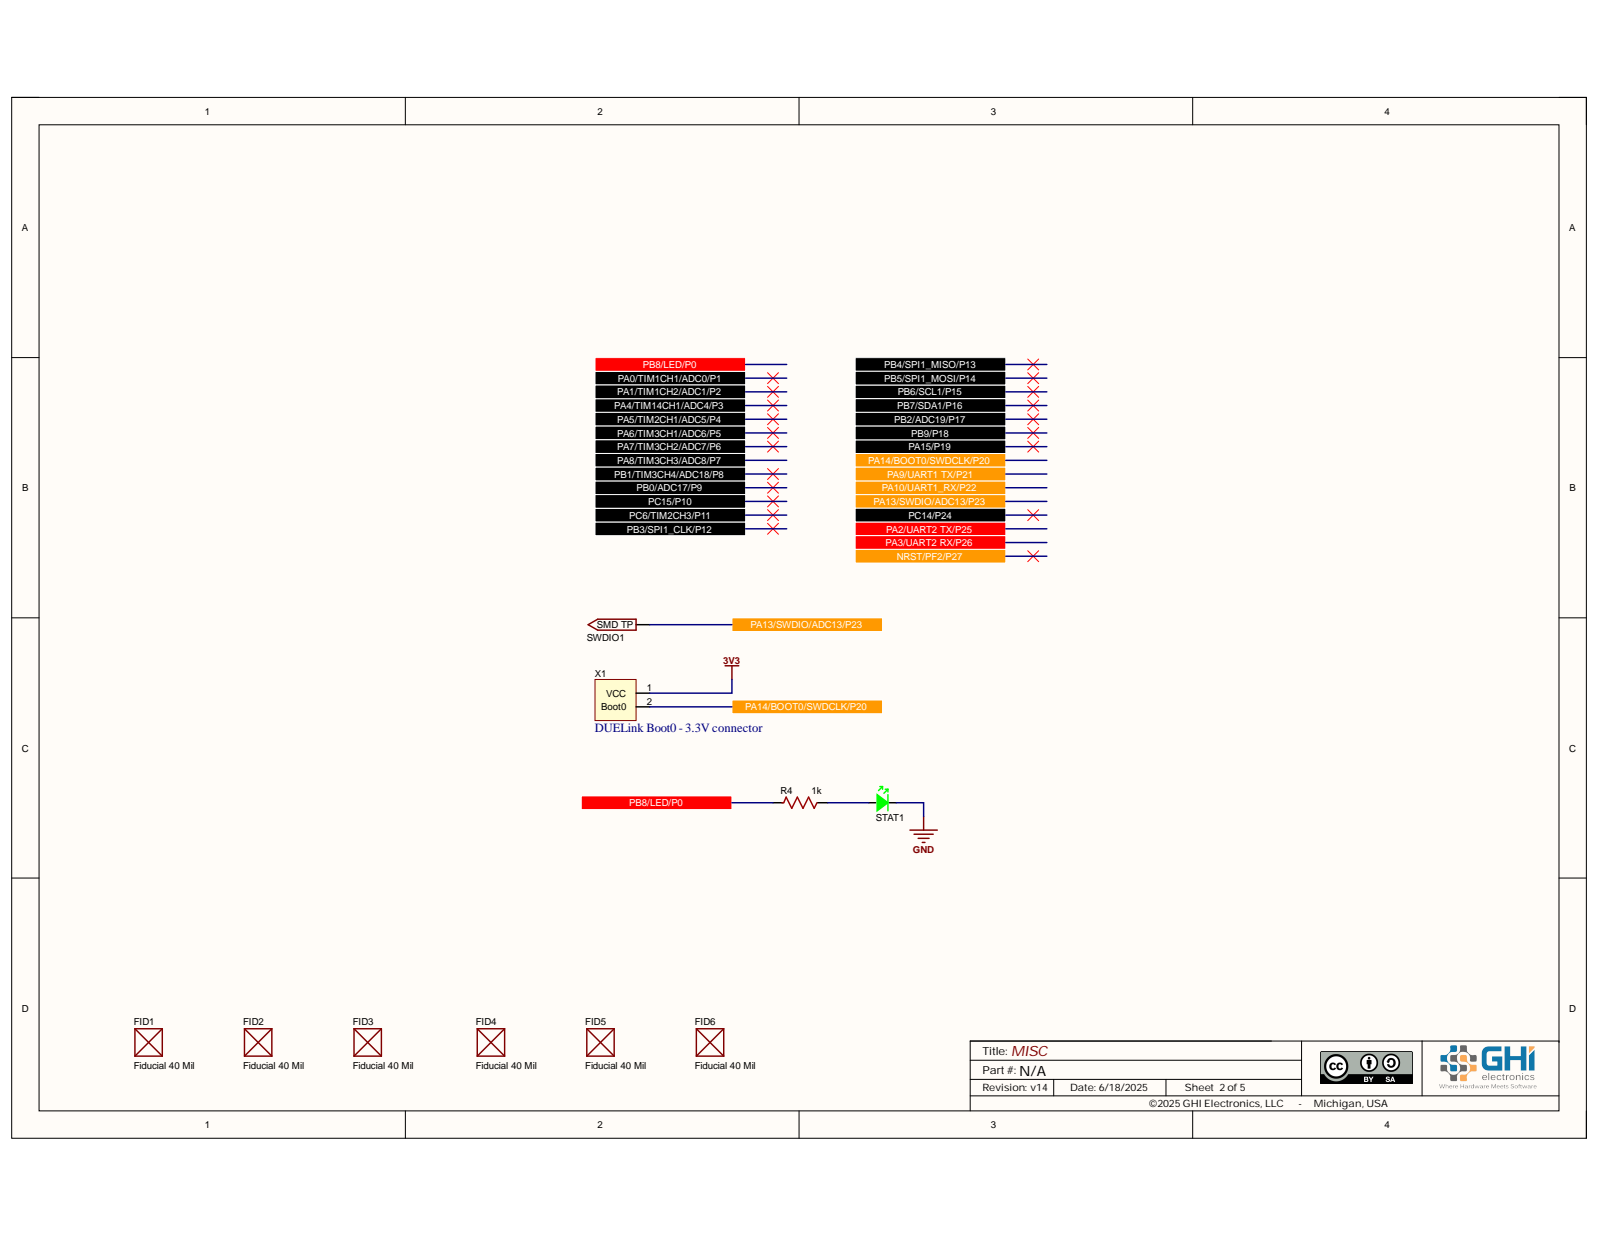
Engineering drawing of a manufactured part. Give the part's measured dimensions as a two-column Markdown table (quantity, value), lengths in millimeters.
| quantity | value |
| --- | --- |
| part name | PCB; Board; STAT1; 0603 LED Green (+5 more) |
| STEP written by | Open CASCADE 7.5 (AUTOMOTIVE_DESIGN) |
| units | millimeters |
| bodies | 89 solids, 1462 faces (1110 planar, 223 cylindrical, 129 other) |
| overall size | 22 × 20 × 9.2 |
| volume | 1 035 mm³ |
| surface area | 1 865 mm² |
| round holes (diameter × count) | 1.02 × 2, 3 × 2, 1.15 × 1 |
| partial cylindrical surfaces (radius × count) | 0.12 × 35, 0.15 × 14, 0.2 × 4, 0.25 × 4, 0.17 × 2, 0.18 × 2, 0.18 × 2, 3.5 × 2 |
| main face-to-face distances | 1.77, 3, 4.77, 1, 0.37, 0.55, 6, 1.15, 0.45, 2.53 |
| hole center spacings | 2.54, 7.14, 11.25, 12.56, 13.87, 13.93, 14.5, 15 |
